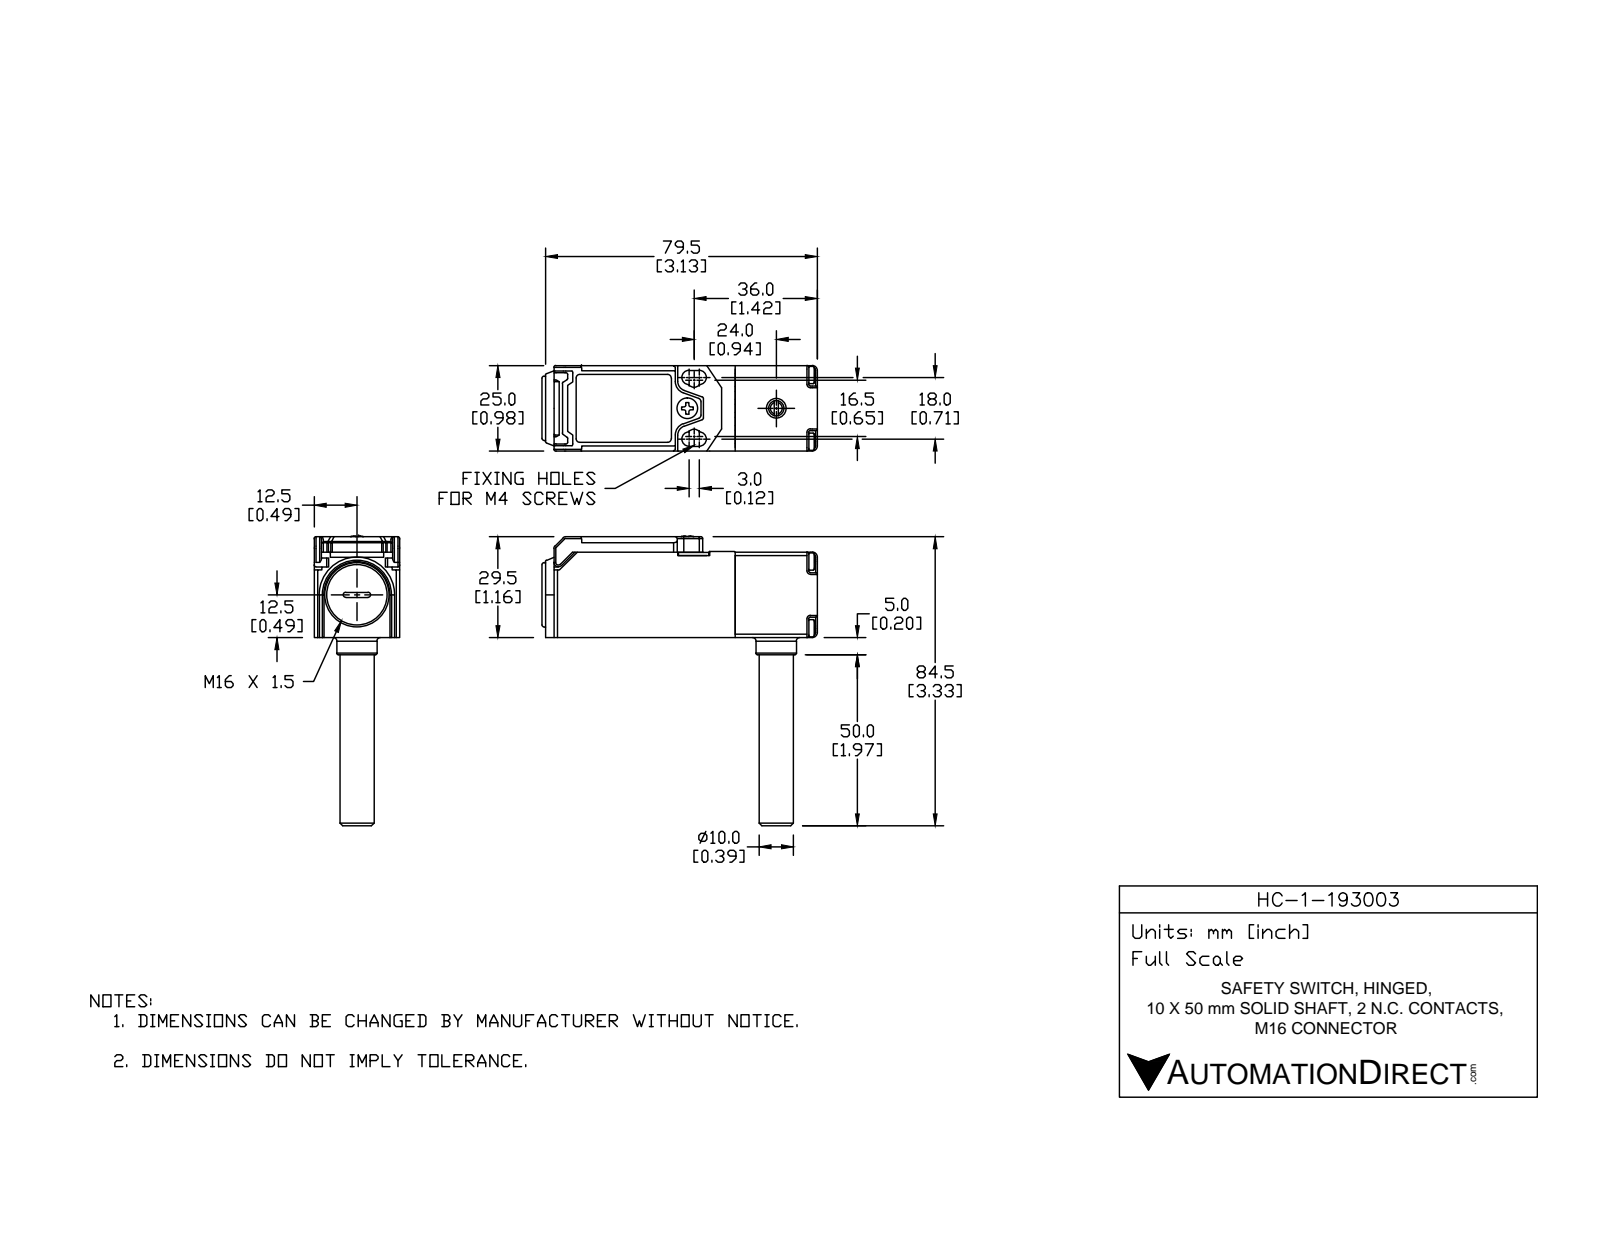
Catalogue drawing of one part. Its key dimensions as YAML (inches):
part_name: "HC-1-193003"
step_written_by: "SolidWorks 2014 (AUTOMOTIVE_DESIGN)"
units: inches
bodies: {solids: 14, faces: 1702, planar: 700, cylindrical: 601, other: 401}
overall_size: [3.336, 3.169, 0.984]
volume: 1.788
surface_area: 43.04
round_holes:
  - {diameter: 0.126, count: 5}
  - {diameter: 0.094, count: 4}
  - {diameter: 0.059, count: 2}
  - {diameter: 0.063, count: 2}
  - {diameter: 0.071, count: 2}
  - {diameter: 0.087, count: 2}
  - {diameter: 0.142, count: 2}
  - {diameter: 0.055, count: 1}
  - {diameter: 0.081, count: 1}
  - {diameter: 0.098, count: 1}
  - {diameter: 0.102, count: 1}
  - {diameter: 0.185, count: 1}
round_bosses_or_shafts:
  - {diameter: 0.102, count: 5}
  - {diameter: 0.197, count: 4}
  - {diameter: 0.079, count: 4}
  - {diameter: 0.138, count: 2}
  - {diameter: 0.74, count: 1}
  - {diameter: 0.531, count: 1}
  - {diameter: 0.394, count: 1}
  - {diameter: 0.386, count: 1}
partial_cylinders:
  - {radius: 0.02, count: 226}
  - {radius: 0.004, count: 24}
  - {radius: 0.012, count: 20}
  - {radius: 0.039, count: 20}
  - {radius: 0.059, count: 7}
  - {radius: 0.083, count: 6}
  - {radius: 0.11, count: 6}
  - {radius: 0.008, count: 4}
face_to_face_distances: [0.984, 0.079, 0.071, 0.913, 0.039, 0.906, 0.945, 0.827, 0.874, 1.15]
hole_center_spacings: [0.543, 0.768, 0.171, 0.187, 0.245, 0.414, 0.423, 0.426]
